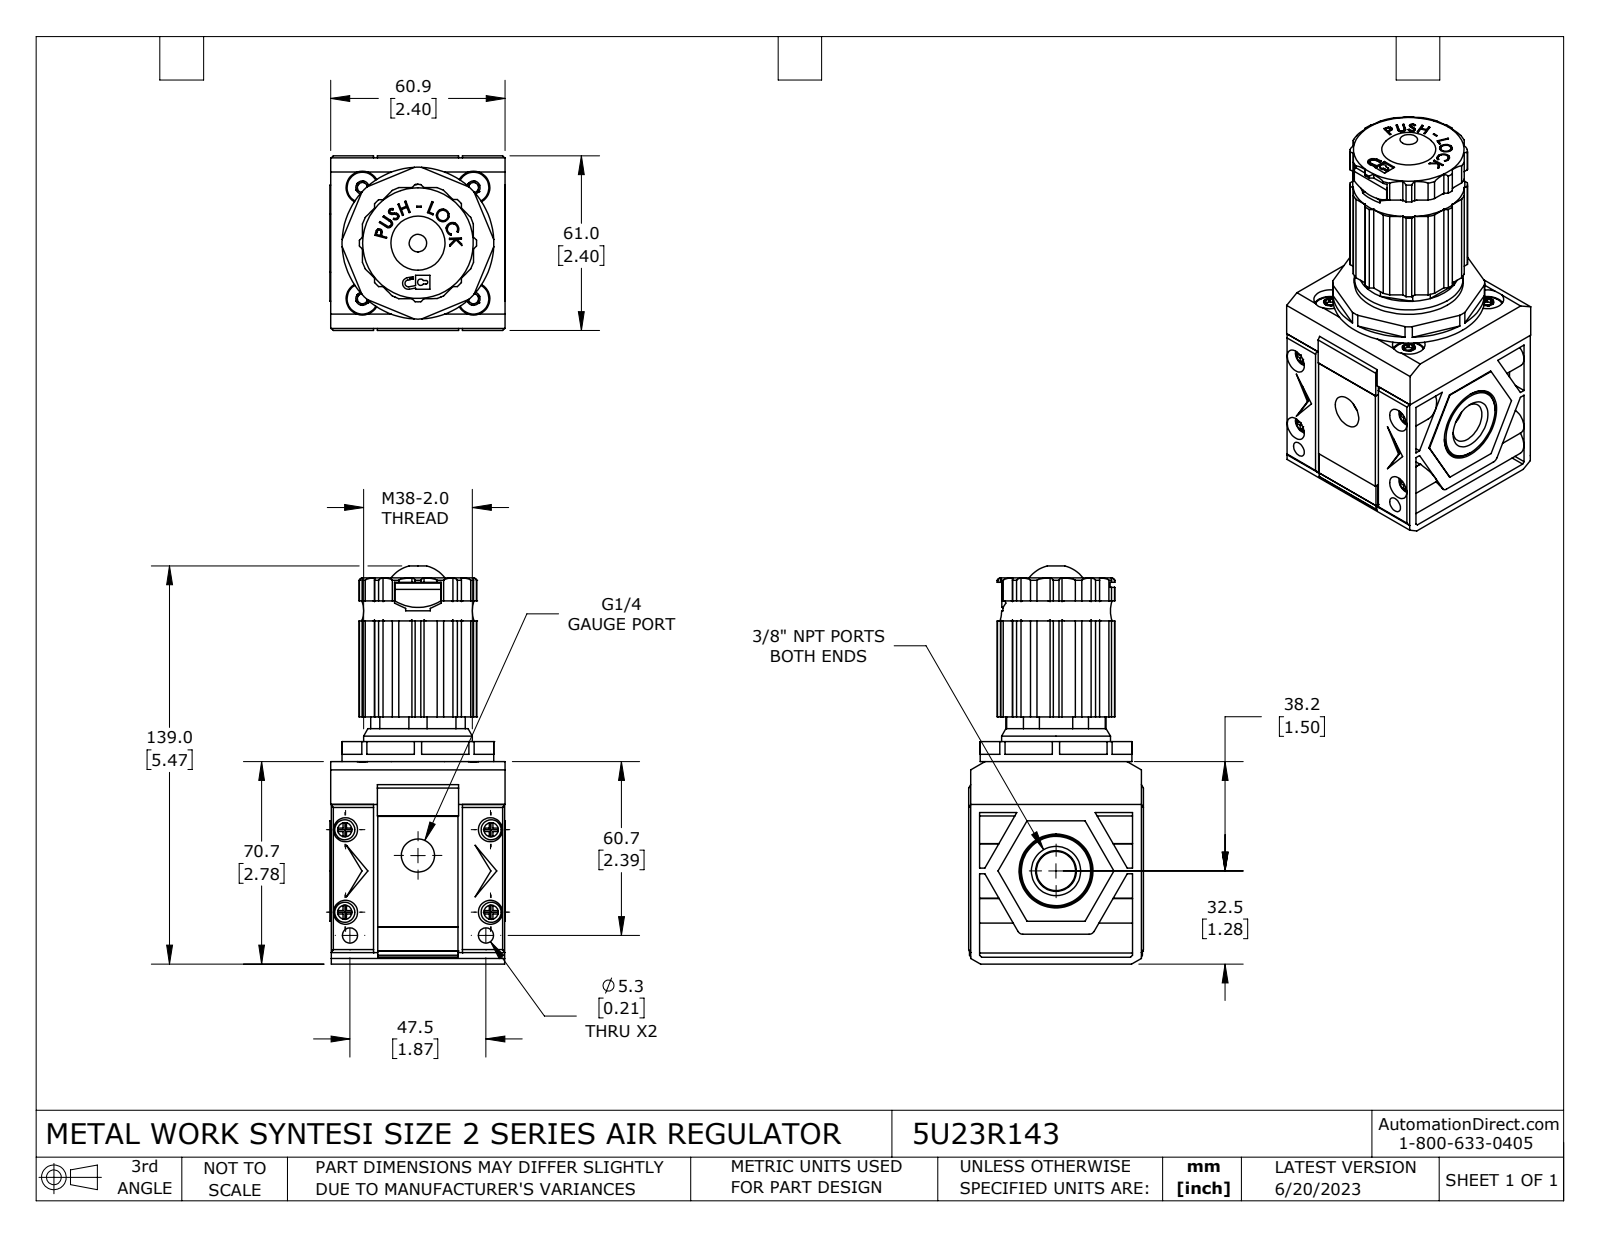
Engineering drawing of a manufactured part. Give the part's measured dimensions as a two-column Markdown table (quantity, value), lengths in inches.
| quantity | value |
| --- | --- |
| part name | 5U23R143 |
| STEP written by | SolidWorks 2021 (CONFIG_CONTROL_DESIGN) |
| units | inches |
| bodies | 13 solids, 1071 faces (610 planar, 329 cylindrical, 132 other) |
| overall size | 5.472 × 2.411 × 2.402 |
| volume | 17.09 in³ |
| surface area | 128.9 in² |
| round holes (diameter × count) | 0.128 × 4, 0.165 × 4, 0.331 × 4, 0.449 × 4, 0.209 × 2, 0.457 × 1, 1.25 × 1, 1.411 × 1, 1.508 × 1 |
| round bosses / shafts (diameter × count) | 0.276 × 4, 0.189 × 4, 0.15 × 4, 2.087 × 1, 1.496 × 1, 1.248 × 1, 1.035 × 1, 0.925 × 1 |
| partial cylindrical surfaces (radius × count) | 0.011 × 28, 0.069 × 4, 0.191 × 4, 0.807 × 4, 0.079 × 2, 0.242 × 2, 0.022 × 1, 0.025 × 1 |
| main face-to-face distances | 2.39, 0.094, 2.193, 2.098, 2.402, 0.591, 2.319, 2.783, 2.689, 1.559 |
| hole center spacings | 1.08, 1.528, 0.325, 1.057, 1.134, 1.265, 1.443, 1.454 |
